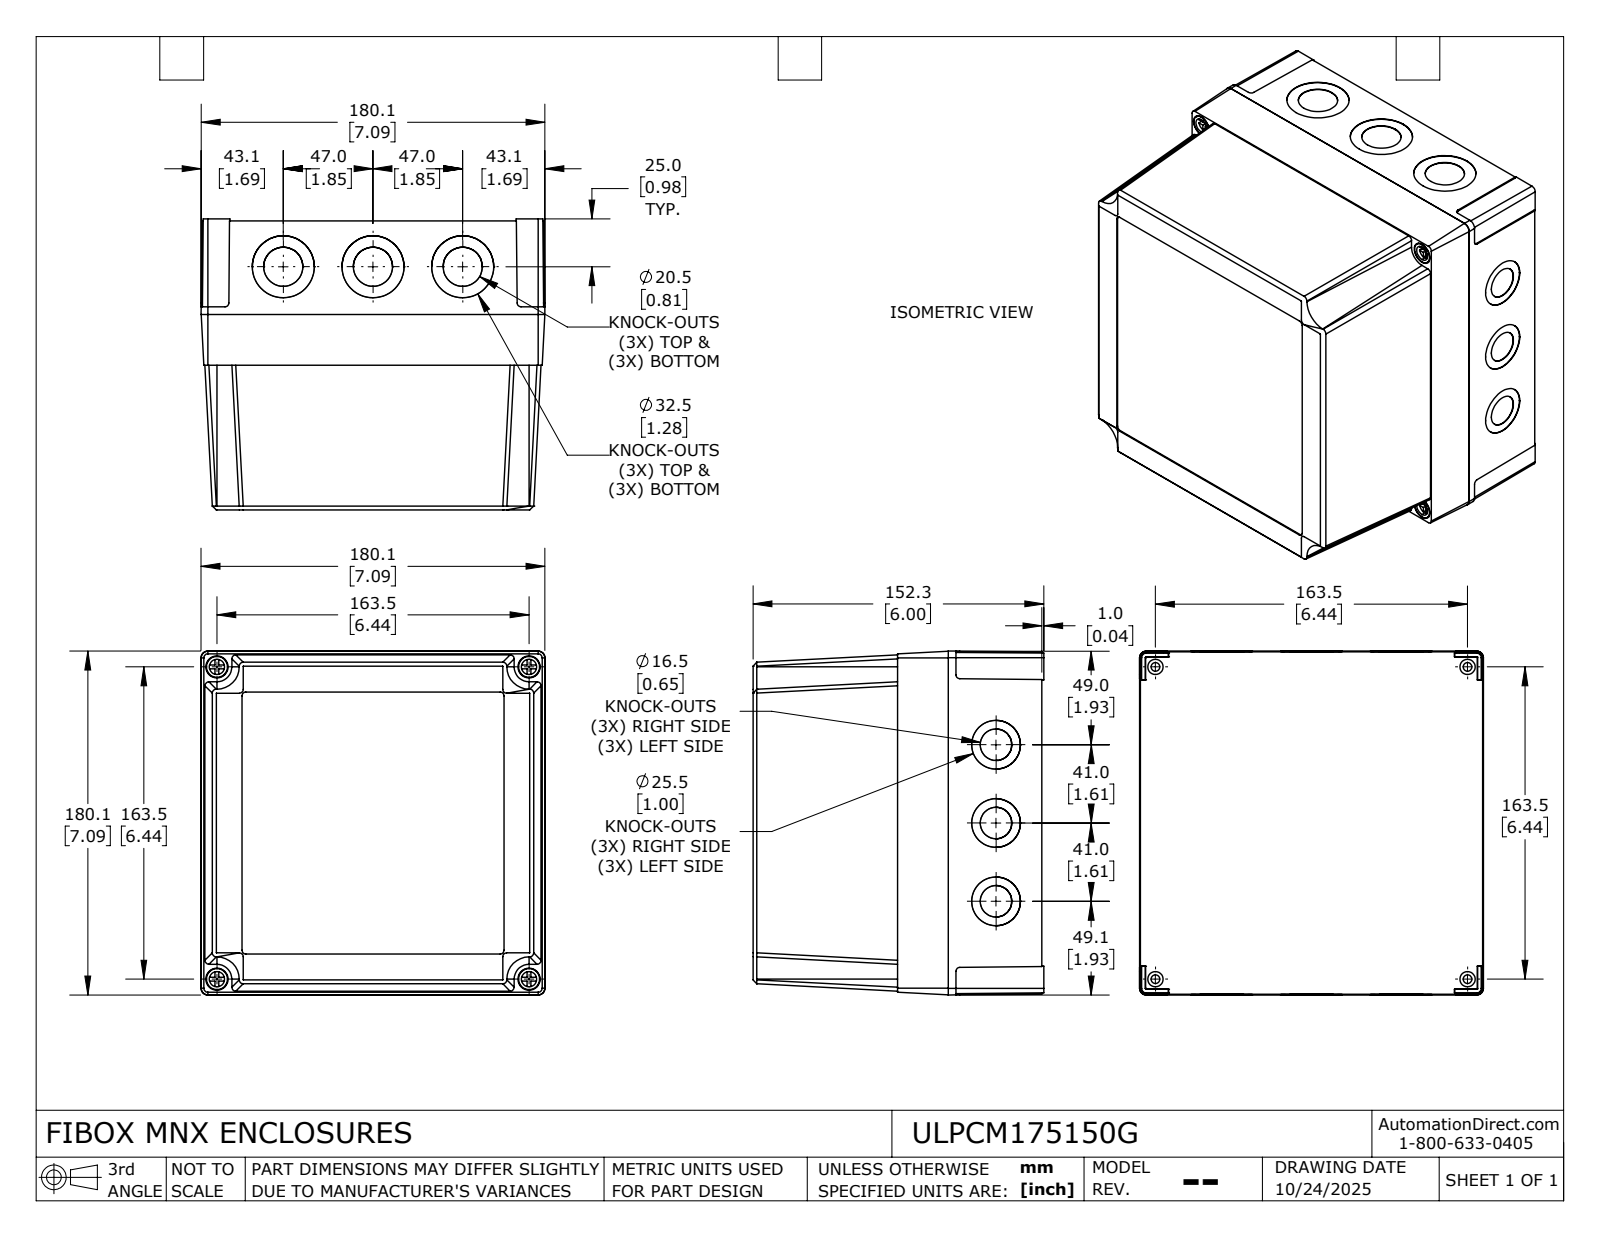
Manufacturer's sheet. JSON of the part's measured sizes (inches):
{"part_name": "ULPCM175150G_Default", "step_written_by": "SolidWorks 2024 (CONFIG_CONTROL_DESIGN)", "units": "inches", "bodies": {"solids": 6, "faces": 633, "planar": 355, "cylindrical": 232, "other": 46}, "overall_size": [7.091, 7.091, 5.996], "volume_in3": 28.98, "surface_area_in2": 529, "round_holes": [[0.126, 12], [0.157, 12], [0.65, 6], [0.807, 6], [1.004, 6], [1.28, 6], [0.177, 4], [0.315, 4], [0.457, 4]], "round_bosses_or_shafts": [[0.315, 12], [0.098, 8], [0.433, 4], [0.283, 4]], "partial_cylinders_radius": [[0.079, 8], [0.083, 8], [0.112, 6], [0.042, 4], [0.197, 4], [0.046, 2]], "face_to_face_distances": [0.079, 0.118, 5.858, 5.74, 0.165, 5.819, 5.937, 0.101, 0.022, 0.098], "hole_center_spacings": [1.333, 1.969, 2.866, 3.252, 4.79, 5.207, 5.469, 5.853]}
